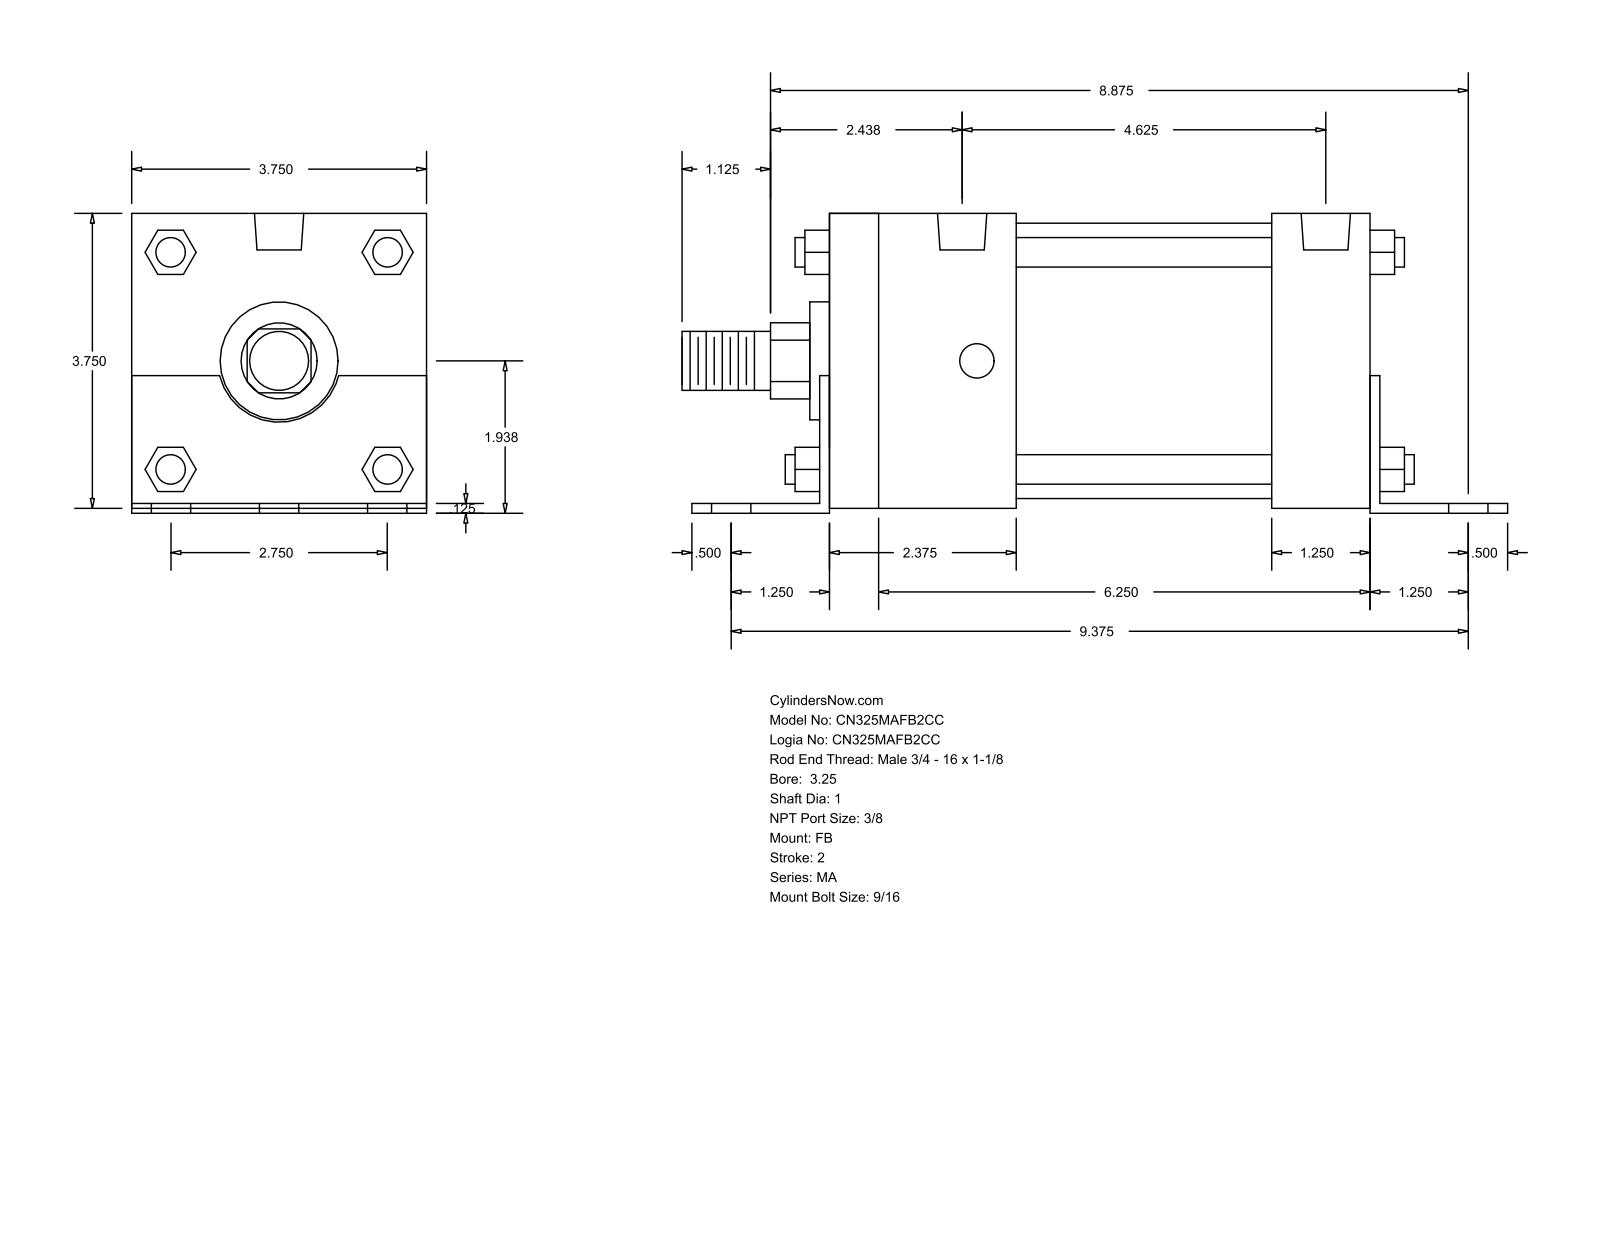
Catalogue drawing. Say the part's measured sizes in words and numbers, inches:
The part is named "MA_FB__0325_1". Its 3-D file was written by "GSSL Pune (CONFIG_CONTROL_DESIGN)". It is 0 solids with 140 faces: 105 planar, 35 cylindrical and 0 other. Overall it measures 10.5 by 3.813 by 3.75 inches. Round holes: 6 of diameter 0.563, 4 of diameter 0.437, 2 of diameter 0.627. Round bosses or shafts: 4 of diameter 0.375, 1 of diameter 3.5, 1 of diameter 1.5, 1 of diameter 1, 1 of diameter 0.75. Partial cylindrical surfaces (rounded edges, fillets, slot ends): 1 of radius 0.484, 1 of radius 0.78. The main face-to-face distances are 3.75, 0.125, 0.063, 3.812, 0.062, 3.687, 7, 6.875, 7.125, 5.75. The hole center spacings are 1.375, 9.476, 9.375, 2.275, 2.427, 2.75, 3.243, 3.414.
